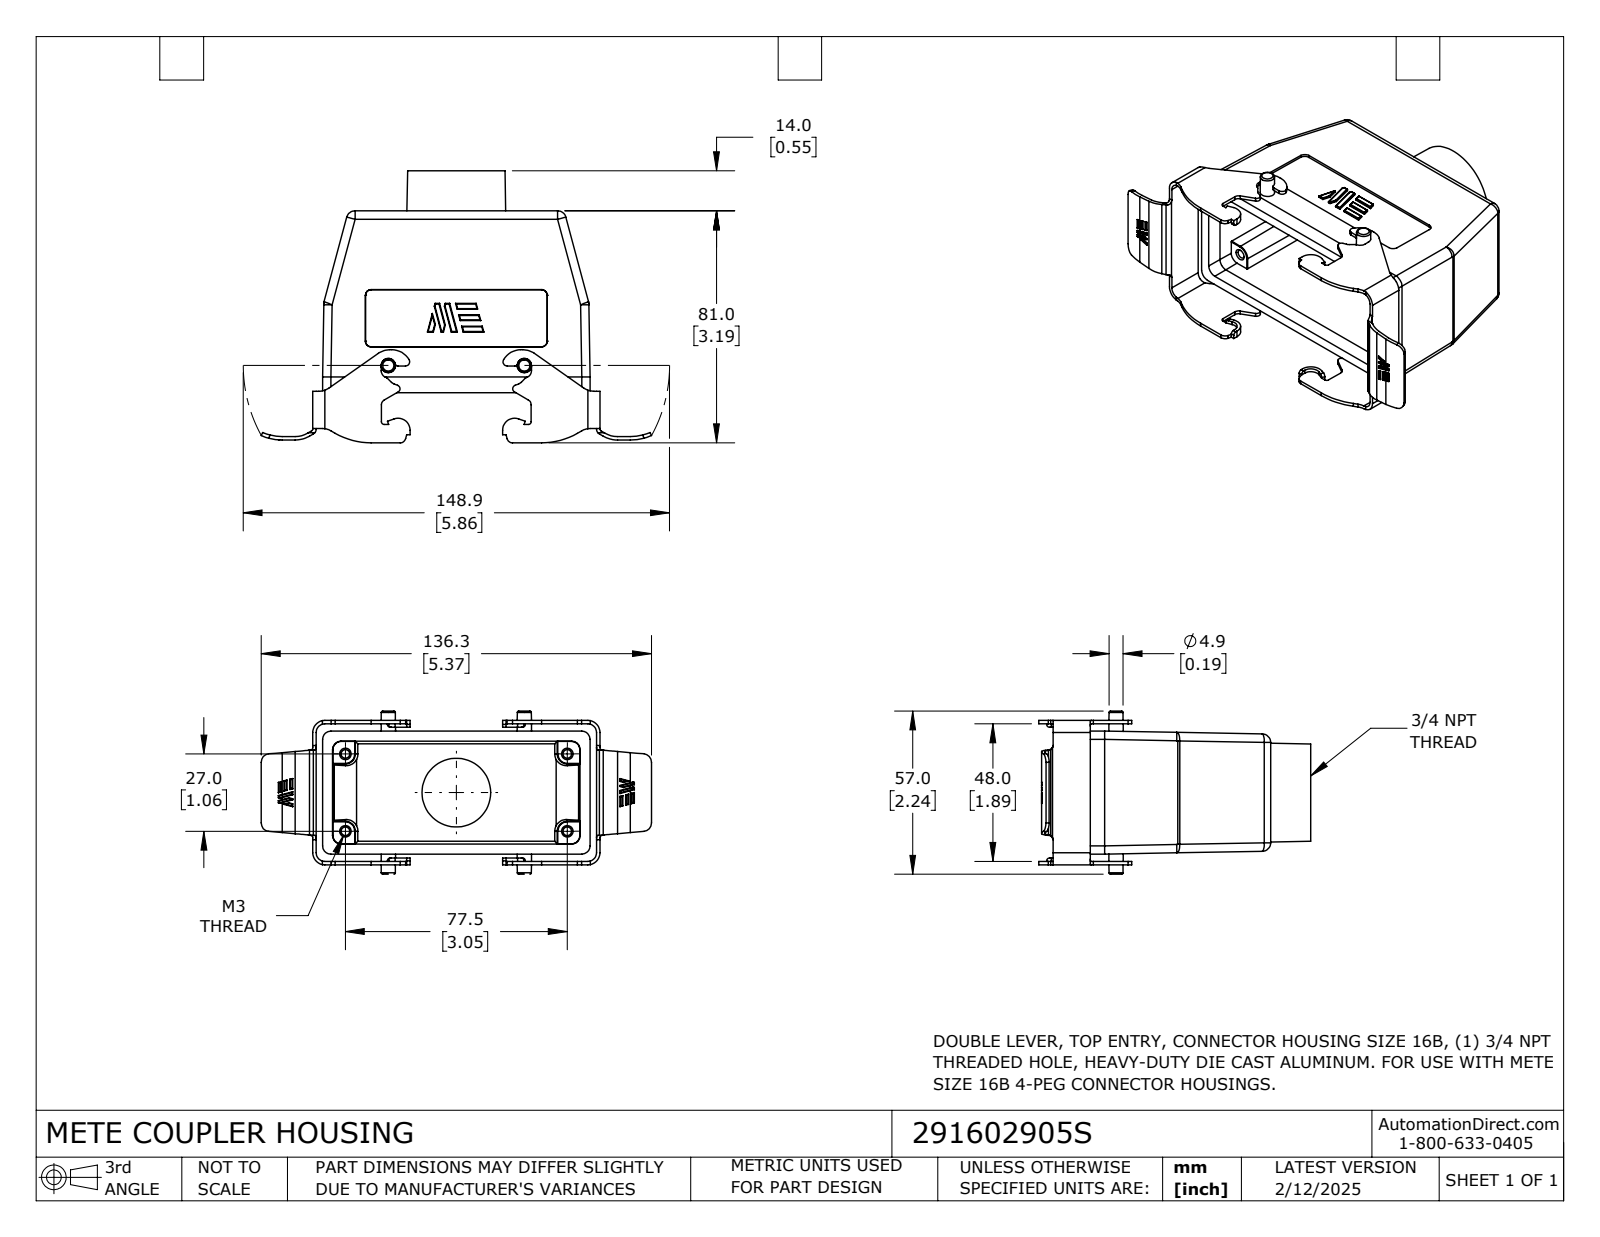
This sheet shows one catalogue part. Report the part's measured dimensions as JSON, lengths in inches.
{"part_name": "291602905S", "step_written_by": "SolidWorks 2024 (CONFIG_CONTROL_DESIGN)", "units": "inches", "bodies": {"solids": 1, "faces": 561, "planar": 245, "cylindrical": 254, "other": 62}, "overall_size": [5.366, 3.74, 2.244], "volume_in3": 4.722, "surface_area_in2": 78.64, "round_holes": [[0.118, 4], [0.945, 1], [1.063, 1]], "partial_cylinders_radius": [[0.008, 71], [0.118, 18], [0.079, 14], [0.039, 10], [0.098, 8], [0.059, 6], [0.114, 6], [0.165, 6]], "face_to_face_distances": [0.138, 0.047, 1.937, 0.031, 0.107, 0.118, 1.89, 0.448, 0.31, 1.984], "hole_center_spacings": [1.615, 1.063, 3.051, 3.231]}
